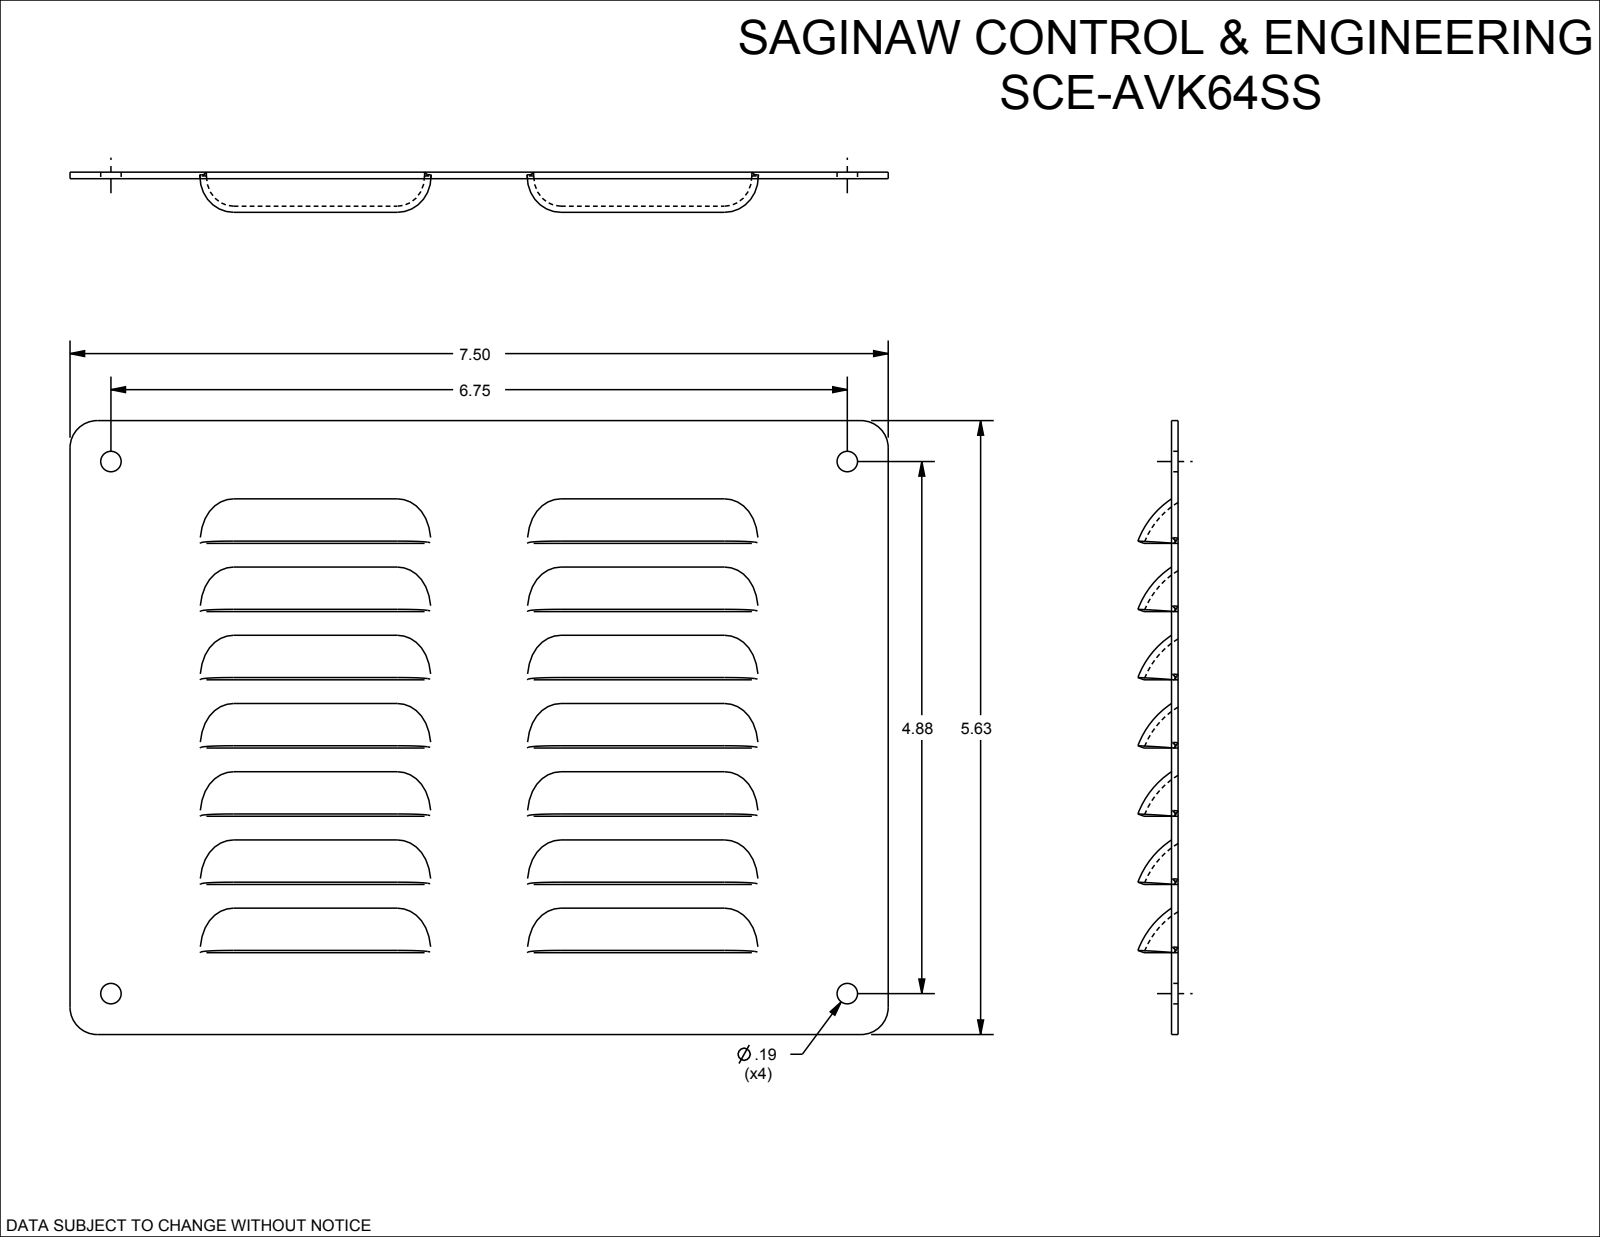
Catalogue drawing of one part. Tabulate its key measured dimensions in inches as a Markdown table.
| quantity | value |
| --- | --- |
| part name | SCE-AVK64_CUT-OUT |
| STEP written by | SolidWorks 2021 (AUTOMOTIVE_DESIGN) |
| units | inches |
| bodies | 1 solid, 228 faces (48 planar, 68 cylindrical, 112 other) |
| overall size | 7.5 × 5.625 × 0.467 |
| volume | 2.788 in³ |
| surface area | 97.91 in² |
| round holes (diameter × count) | 0.187 × 4 |
| partial cylindrical surfaces (radius × count) | 0.74 × 7, 0.8 × 7, 0.25 × 4 |
| main face-to-face distances | 0.06, 1.25, 0.625, 0.625, 2.5, 0.29, 0.96, 1.171, 1.875, 1.875 |
| hole center spacings | 4.875, 6.75, 8.326 |
